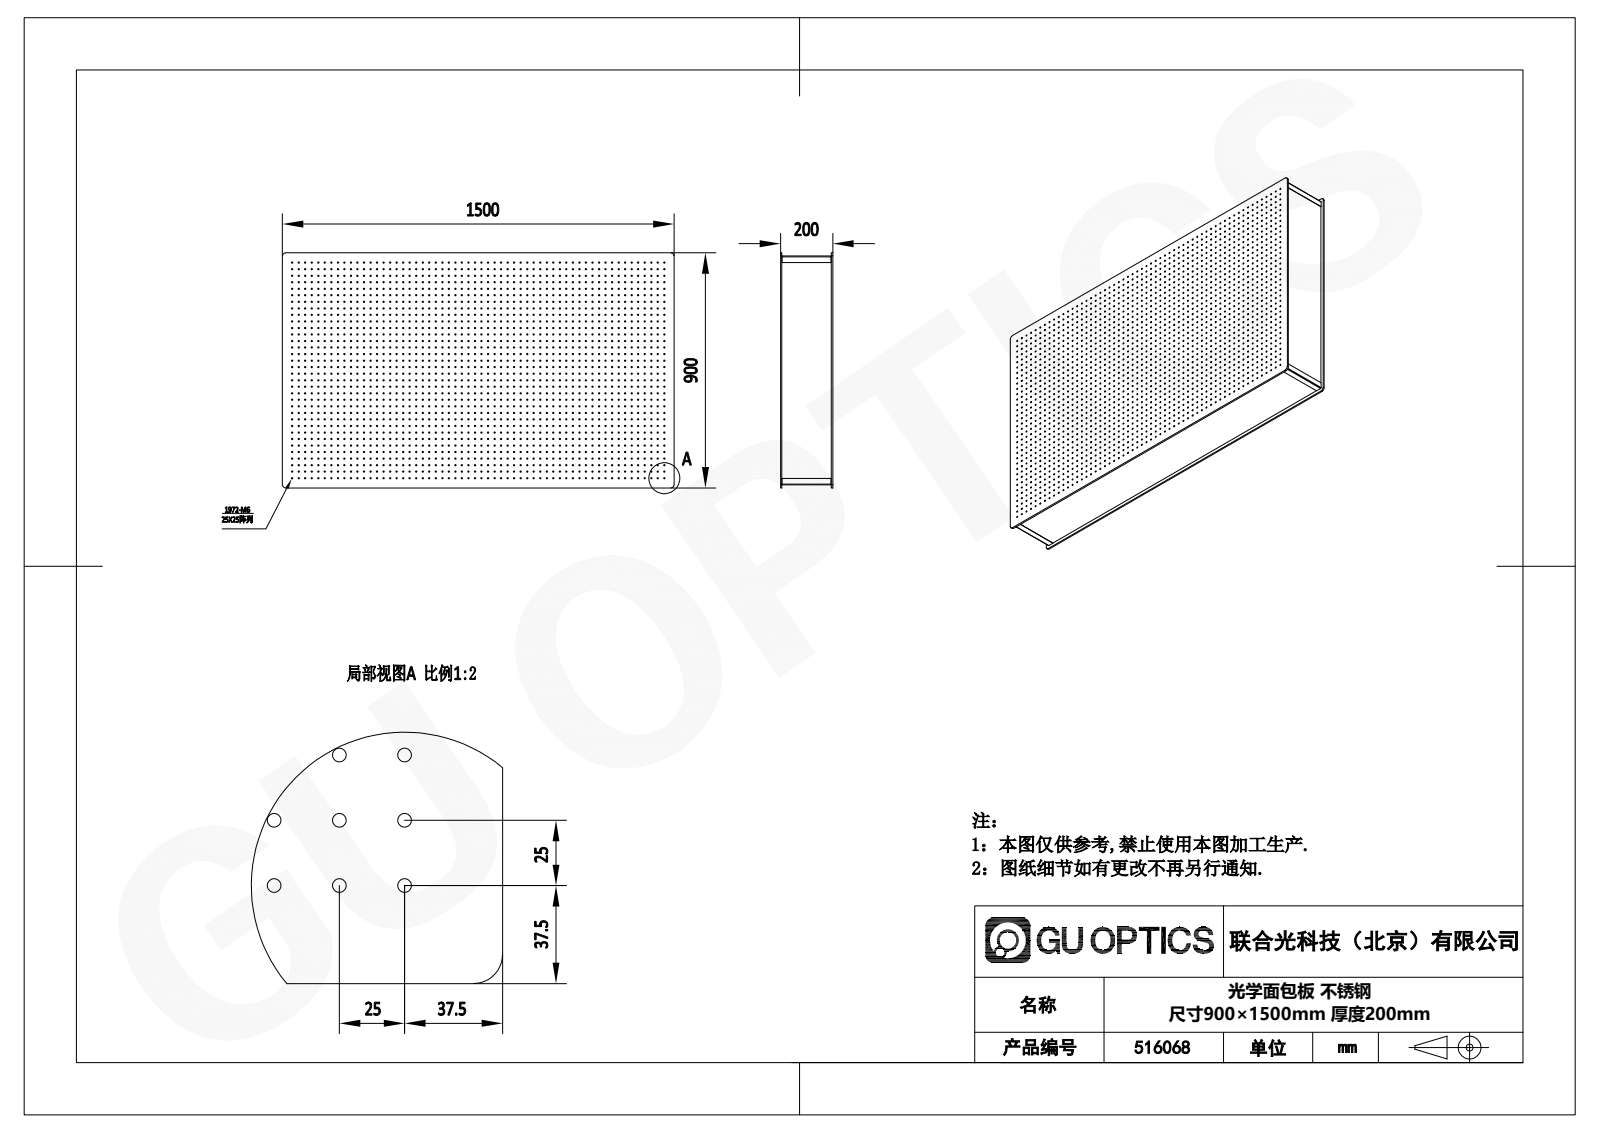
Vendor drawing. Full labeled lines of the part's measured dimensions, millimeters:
Part name (STEP PRODUCT): 516068
STEP written by: SolidWorks 2020 (AUTOMOTIVE_DESIGN)
Units: millimetres
Bodies: 1 solid, 5976 faces (2016 planar, 3960 cylindrical, 0 other)
Overall size (bounding box): 1500 × 900 × 200
Volume: 258 100 000 mm³ · Surface area: 3 999 000 mm²
Round holes (diameter × count): ⌀5.3 ×1972
Partial cylindrical surfaces — rounded edges, fillets, slot ends (radius × count): R2 ×4, R3 ×4, R11 ×4
Main face-to-face distances: 200, 874, 1474, 6, 194, 195, 189, 5, 13, 1
Hole centre spacings: 79.06, 55.9, 35.36, 50, 25, 90.14, 103.08, 70.71
